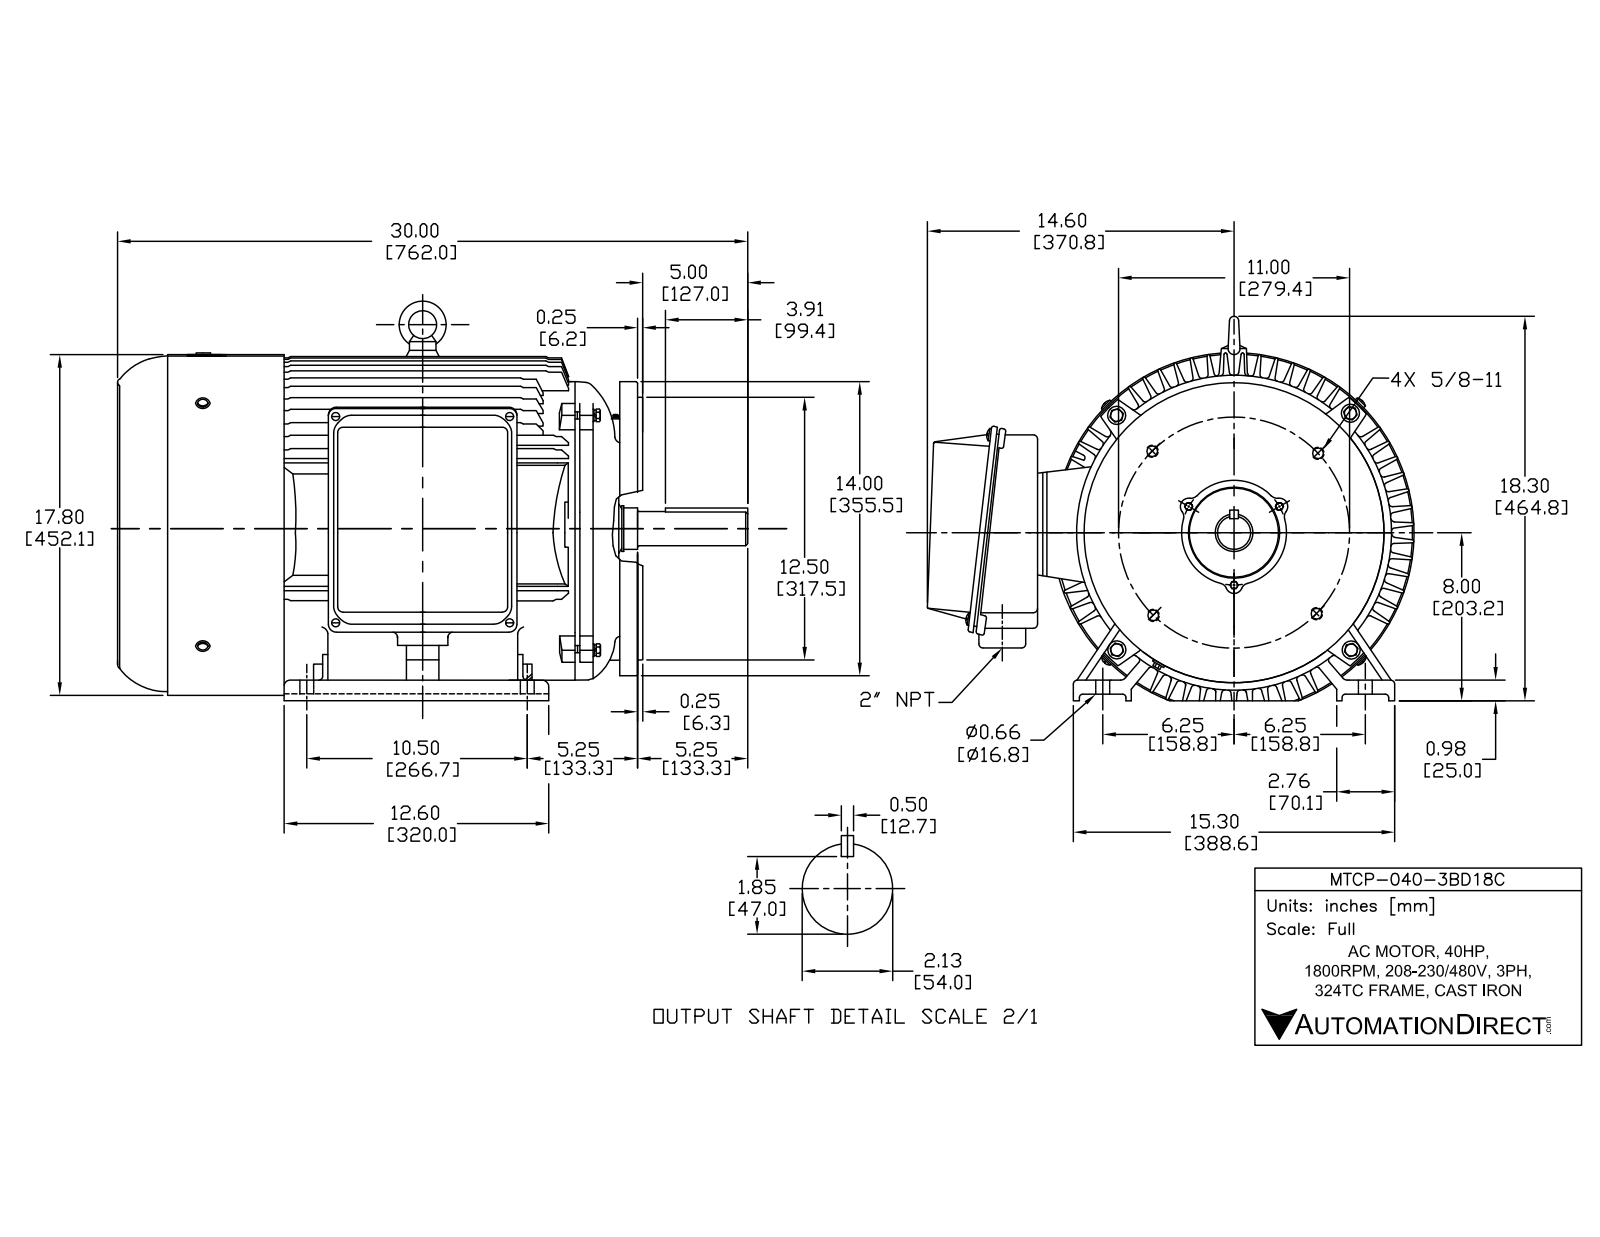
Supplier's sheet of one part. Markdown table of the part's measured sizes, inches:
| quantity | value |
| --- | --- |
| part name | PE320接线盒座_默认_按加工; 17橡皮塞; eyebolts gb_GB_FASTENER_SCREWS_FRS M16-N; hexagon head bolts-full thread gb_GB_FASTENER_BOLT_STBAB A M8X20-N (+8 more) |
| STEP written by | SolidWorks 2017 (AUTOMOTIVE_DESIGN) |
| units | inches |
| bodies | 68 solids, 4164 faces (1086 planar, 1465 cylindrical, 1613 other) |
| overall size | 29.232 × 23.004 × 20.37 |
| volume | 1 008 in³ |
| surface area | 6 047 in² |
| round holes (diameter × count) | 0.394 × 21, 0.268 × 8, 0.081 × 4, 0.197 × 4, 0.252 × 4, 0.263 × 4, 0.354 × 4, 0.402 × 4, 0.448 × 4, 0.508 × 4, 0.512 × 4, 0.531 × 4 |
| round bosses / shafts (diameter × count) | 0.315 × 11, 0.472 × 8, 0.945 × 4, 0.752 × 4, 0.389 × 4, 0.236 × 4, 0.394 × 2, 17.52 × 1 |
| partial cylindrical surfaces (radius × count) | 0.039 × 223, 0.197 × 104, 0.118 × 80, 0.079 × 76, 0.02 × 48, 0.059 × 35, 0.394 × 27, 0.315 × 24 |
| main face-to-face distances | 0.236, 0.059, 4.878, 24.236, 24.177, 0.197, 17.598, 0.965, 0.984, 23.272 |
| hole center spacings | 3.937, 8.189, 2.953, 9.832, 2.65, 2.756, 4, 5.352 |
